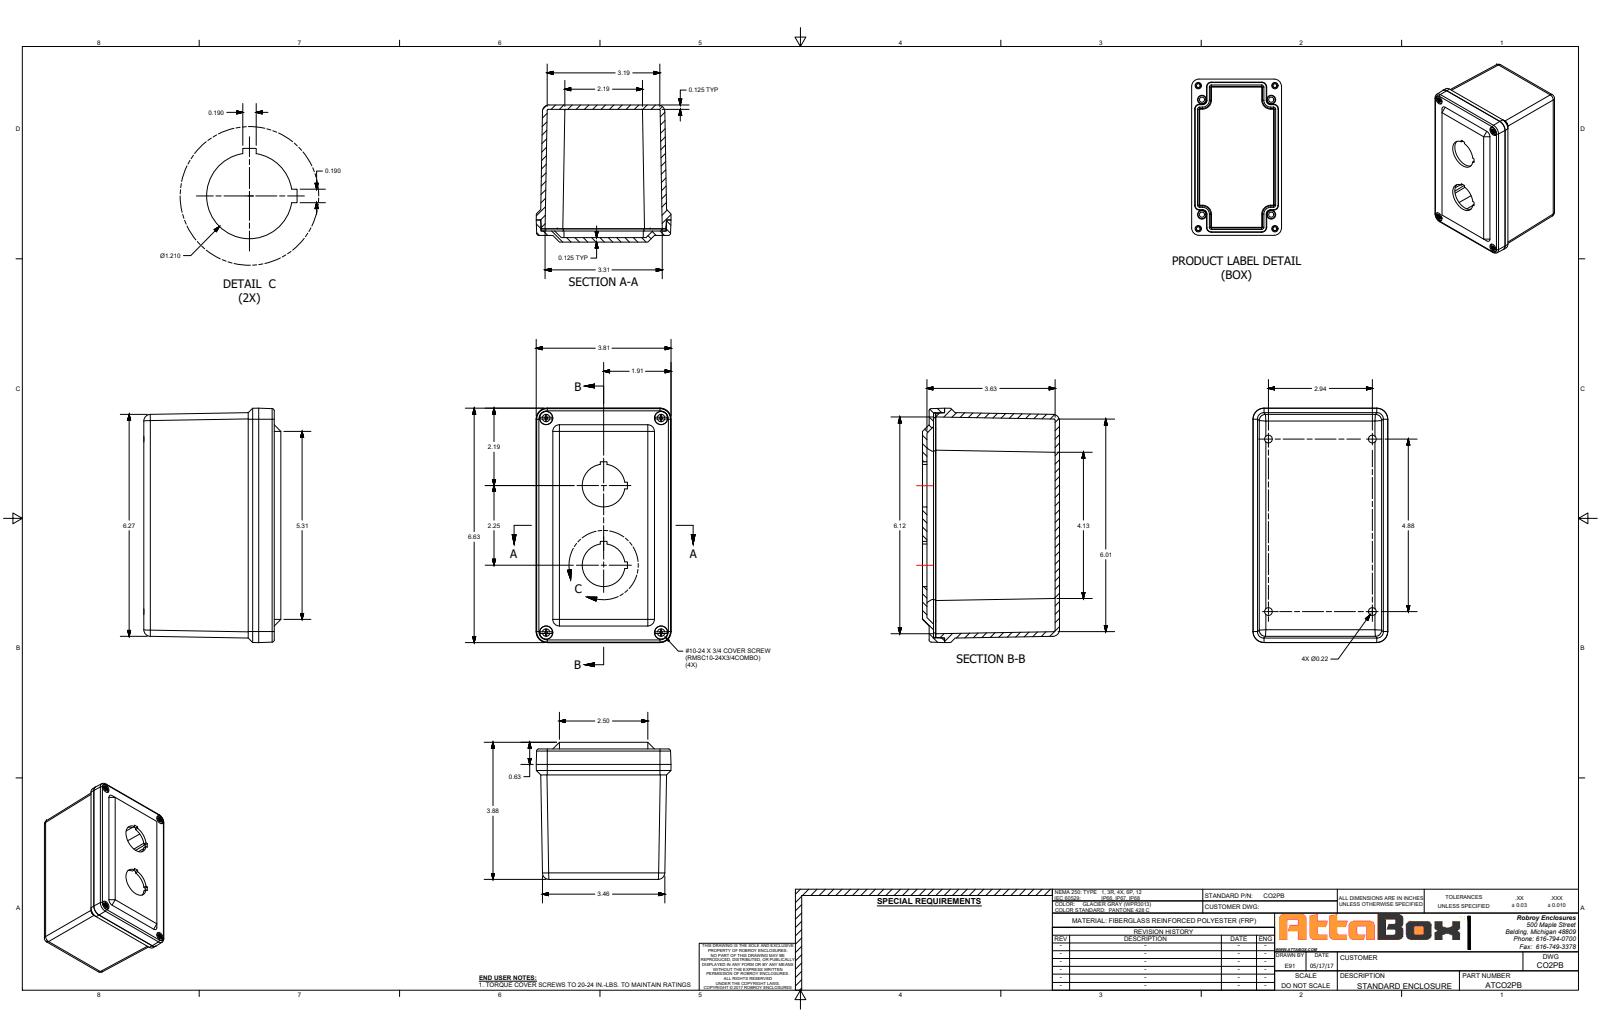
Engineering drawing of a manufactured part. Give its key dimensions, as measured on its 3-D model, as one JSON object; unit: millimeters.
{"part_name": "CO2PB", "step_written_by": "SolidWorks 2018 (AUTOMOTIVE_DESIGN)", "units": "millimeters", "bodies": {"solids": 11, "faces": 395, "planar": 195, "cylindrical": 104, "other": 96}, "overall_size": [168.3, 98.4, 96.8], "volume_mm3": 328600, "surface_area_mm2": 170300, "round_holes": [[5.6, 8], [4, 4], [4.8, 4], [9.5, 4], [30.7, 2]], "round_bosses_or_shafts": [[9.4, 4], [6.9, 4], [4.5, 4]], "partial_cylinders_radius": [[0.8, 20], [0.3, 16], [4.5, 4], [5.6, 4], [8, 4], [8.3, 4], [1.6, 2], [1.6, 2]], "face_to_face_distances": [3.2, 3.3, 95.3, 4.7, 90.5, 12.7, 98.4, 92.1, 1.6, 87.3], "hole_center_spacings": [15.6, 50, 63.6, 80, 97.9, 113.3, 139, 159.6]}
